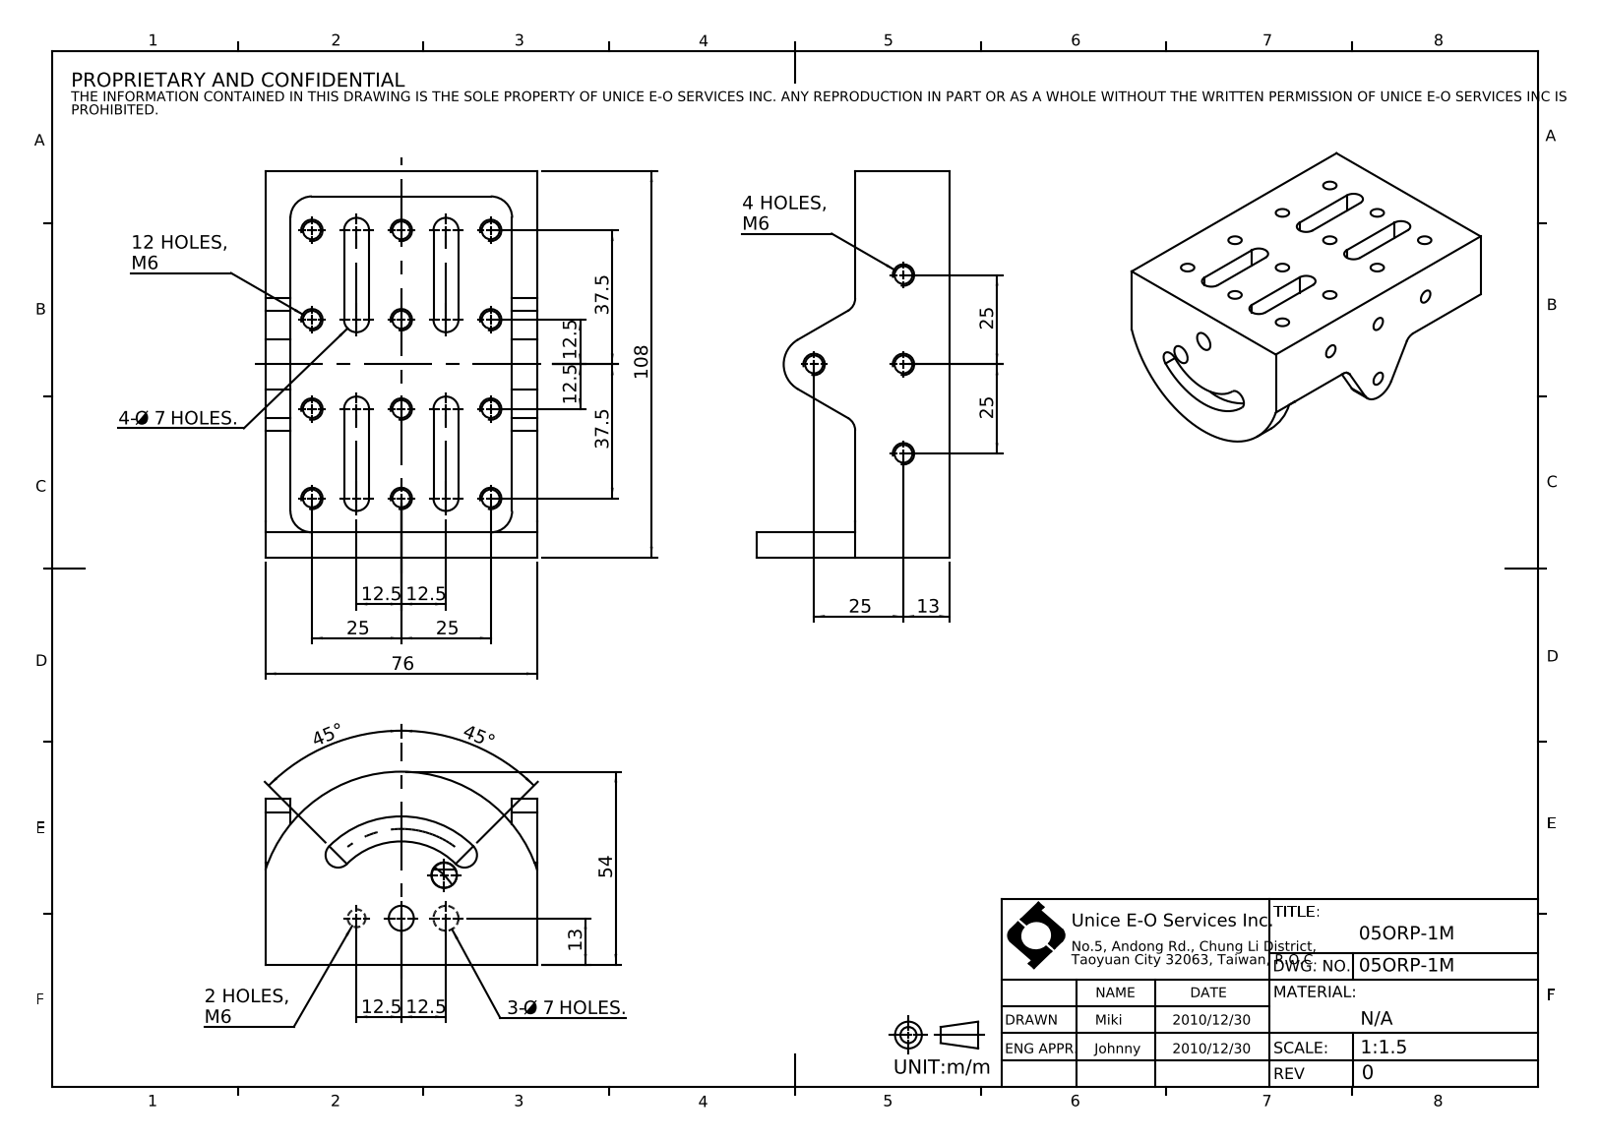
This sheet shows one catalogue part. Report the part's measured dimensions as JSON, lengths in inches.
{"part_name": "05ORP-1M", "step_written_by": "SolidWorks 2016 (CONFIG_CONTROL_DESIGN)", "units": "inches", "bodies": {"solids": 1, "faces": 103, "planar": 27, "cylindrical": 76, "other": 0}, "overall_size": [4.252, 2.992, 2.126], "volume_in3": 6.656, "surface_area_in2": 60.94, "round_holes": [[0.197, 17], [0.276, 3]], "partial_cylinders_radius": [[0.138, 10], [0.236, 4], [0.157, 2], [0.315, 1], [0.846, 1], [1.122, 1], [1.575, 1]], "face_to_face_distances": [0.276, 2.717, 2.992, 3.976, 4.252, 2.441, 0.866, 1.85, 0.768, 1.043], "hole_center_spacings": [0.984, 1.392, 2.201, 1.969, 2.784, 3.113, 2.953, 0.492]}
